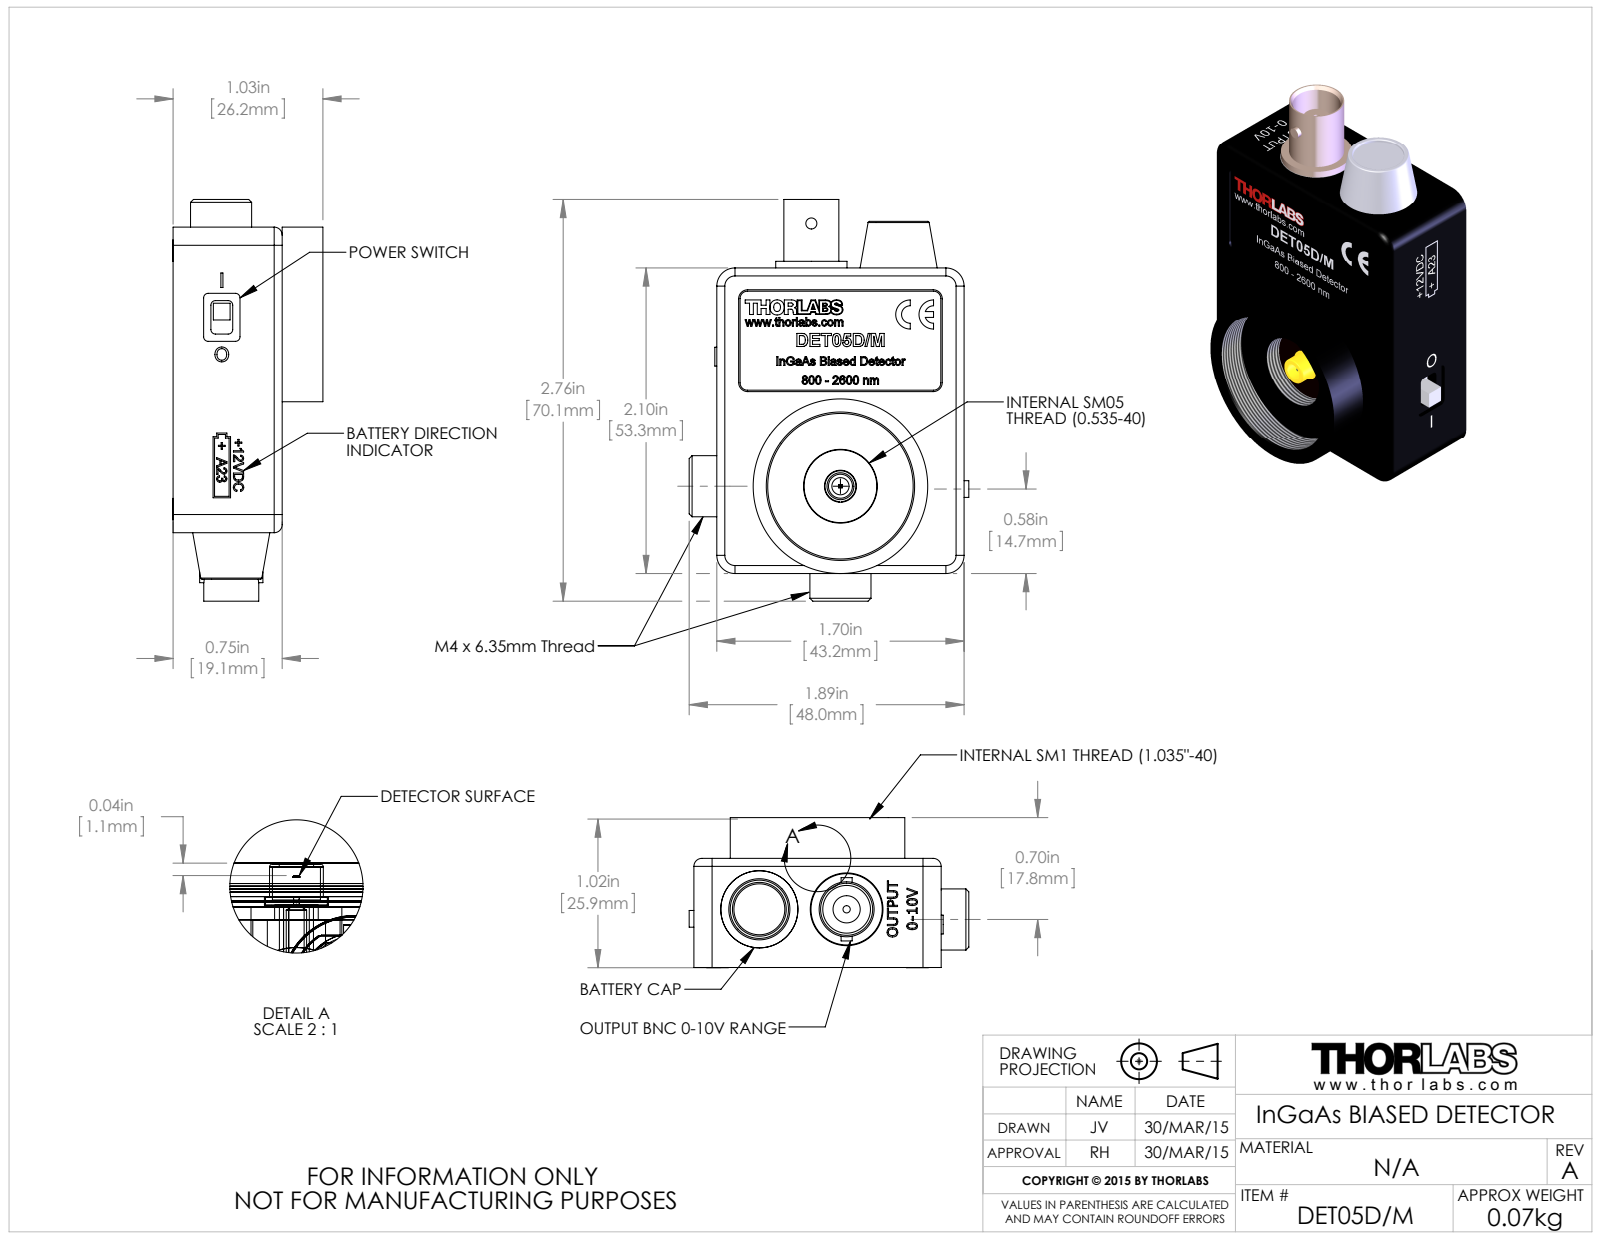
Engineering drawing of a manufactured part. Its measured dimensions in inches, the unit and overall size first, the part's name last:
Units: inches
Overall size (bounding box): 2.761 × 1.922 × 1.032
Round holes (diameter × count): ⌀0.07 ×7, ⌀0.2 ×5, ⌀0.096 ×4, ⌀0.125 ×4, ⌀0.15 ×4, ⌀0.136 ×2, ⌀0.23 ×2, ⌀0.017 ×1, ⌀0.05 ×1, ⌀0.05 ×1, ⌀0.052 ×1, ⌀0.118 ×1
Round bosses / shafts (diameter × count): ⌀0.147 ×4, ⌀0.086 ×4, ⌀0.039 ×4, ⌀0.018 ×3, ⌀0.42 ×2, ⌀0.236 ×2, ⌀1.2 ×1, ⌀1.035 ×1
Partial cylindrical surfaces — rounded edges, fillets, slot ends (radius × count): R0.125 ×26, R0.031 ×8, R0.095 ×8, R0.004 ×6, R0.02 ×6, R0.016 ×4, R0.05 ×4, R0.055 ×4
Main face-to-face distances: 0.063, 0.1, 0.05, 0.07, 0.68, 0.617, 0.02, 0.73, 0.667, 0.75
Hole centre spacings: 0.689, 0.788, 0.815, 0.883, 0.893, 1.066, 1.375, 1.504
Volume: 1.258 in³ · Surface area: 36.74 in²
Bodies: 17 solids, 2159 faces (1185 planar, 268 cylindrical, 706 other)
Part name (STEP PRODUCT): DET housing; TTN035587-LB1_PDA25K-LB1; TTN035503; FD05D
STEP written by: SolidWorks 2014 (AUTOMOTIVE_DESIGN)
